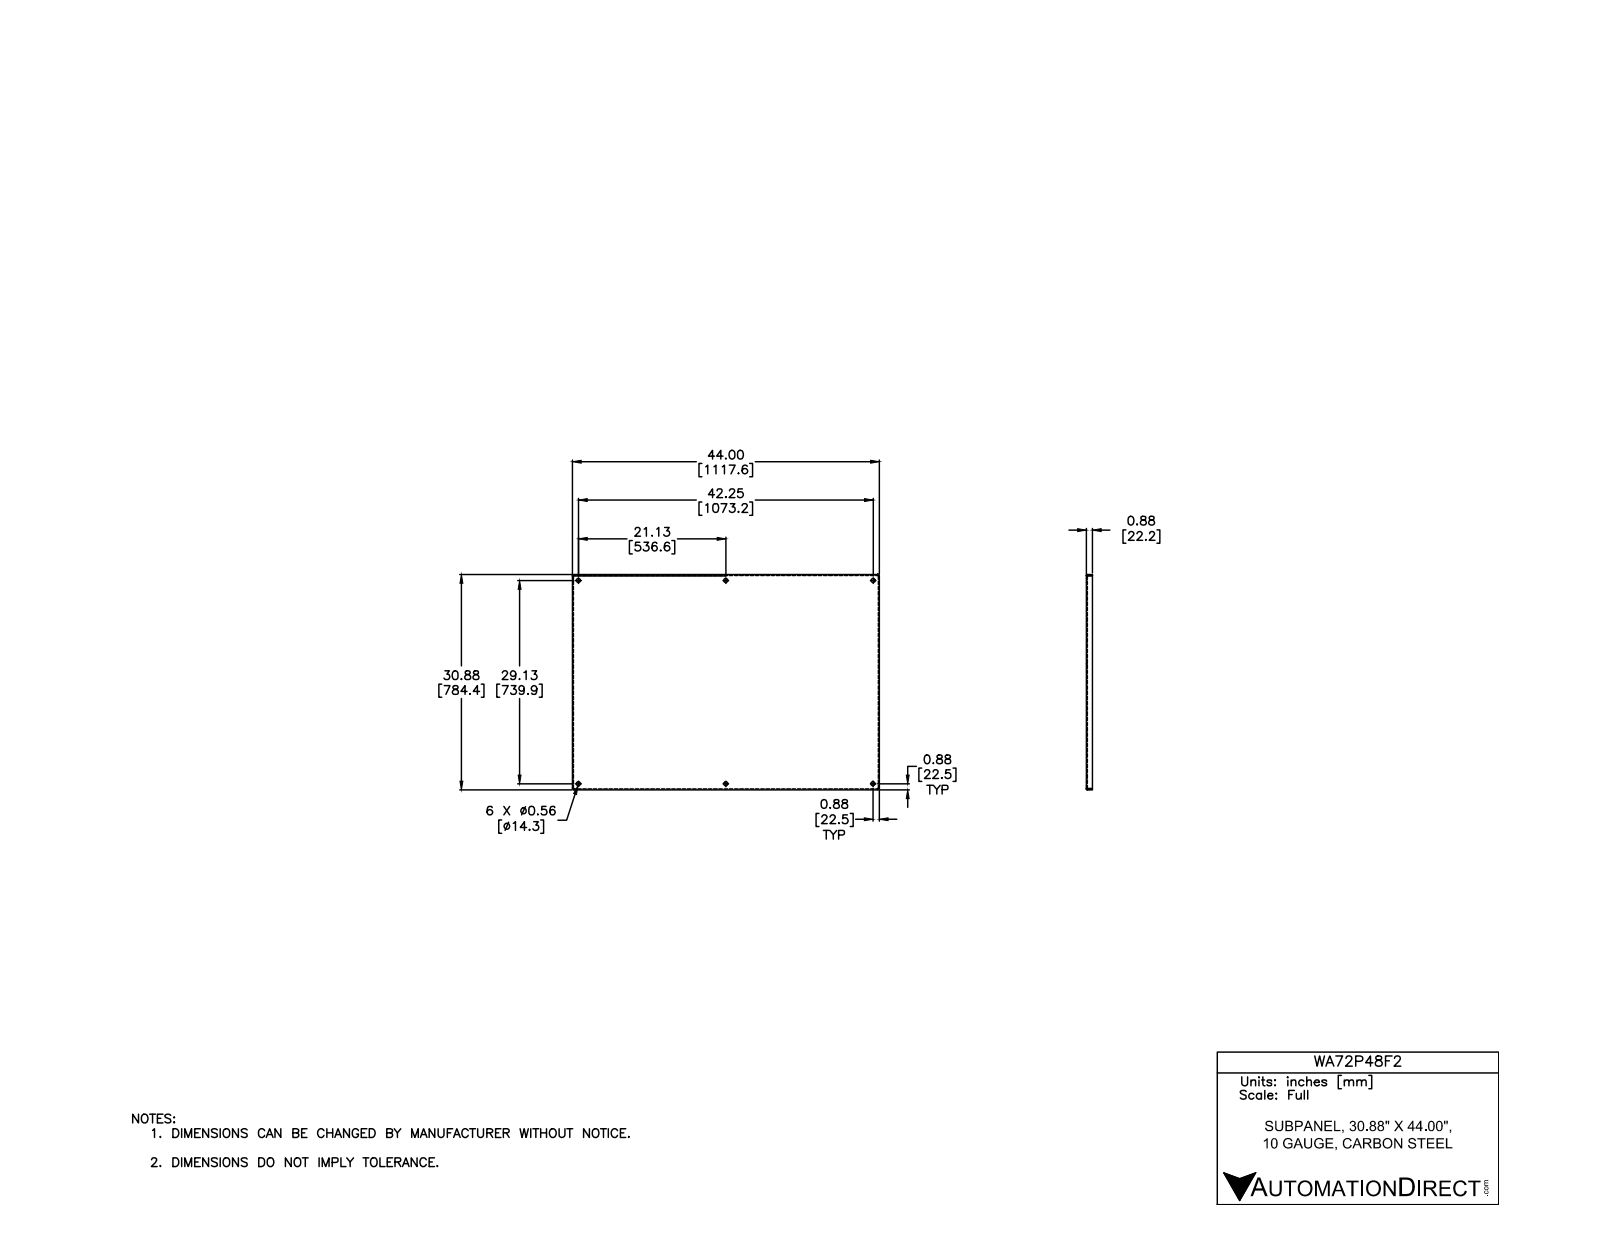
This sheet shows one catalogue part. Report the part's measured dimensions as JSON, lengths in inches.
{"part_name": "WA_P_F", "step_written_by": "Autodesk Inventor 2012 (AUTOMOTIVE_DESIGN)", "units": "inches", "bodies": {"solids": 1, "faces": 44, "planar": 22, "cylindrical": 14, "other": 8}, "overall_size": [44, 30.88, 0.875], "volume_in3": 182.8, "surface_area_in2": 2945, "round_holes": [[0.563, 6]], "partial_cylinders_radius": [[0.031, 4], [0.156, 4]], "face_to_face_distances": [0.125, 0.125, 43.875, 30.755, 30.88, 30.63, 30.755, 44, 43.75, 0.75], "hole_center_spacings": [21.125, 35.984, 29.13, 42.25, 51.319, 29.13]}
